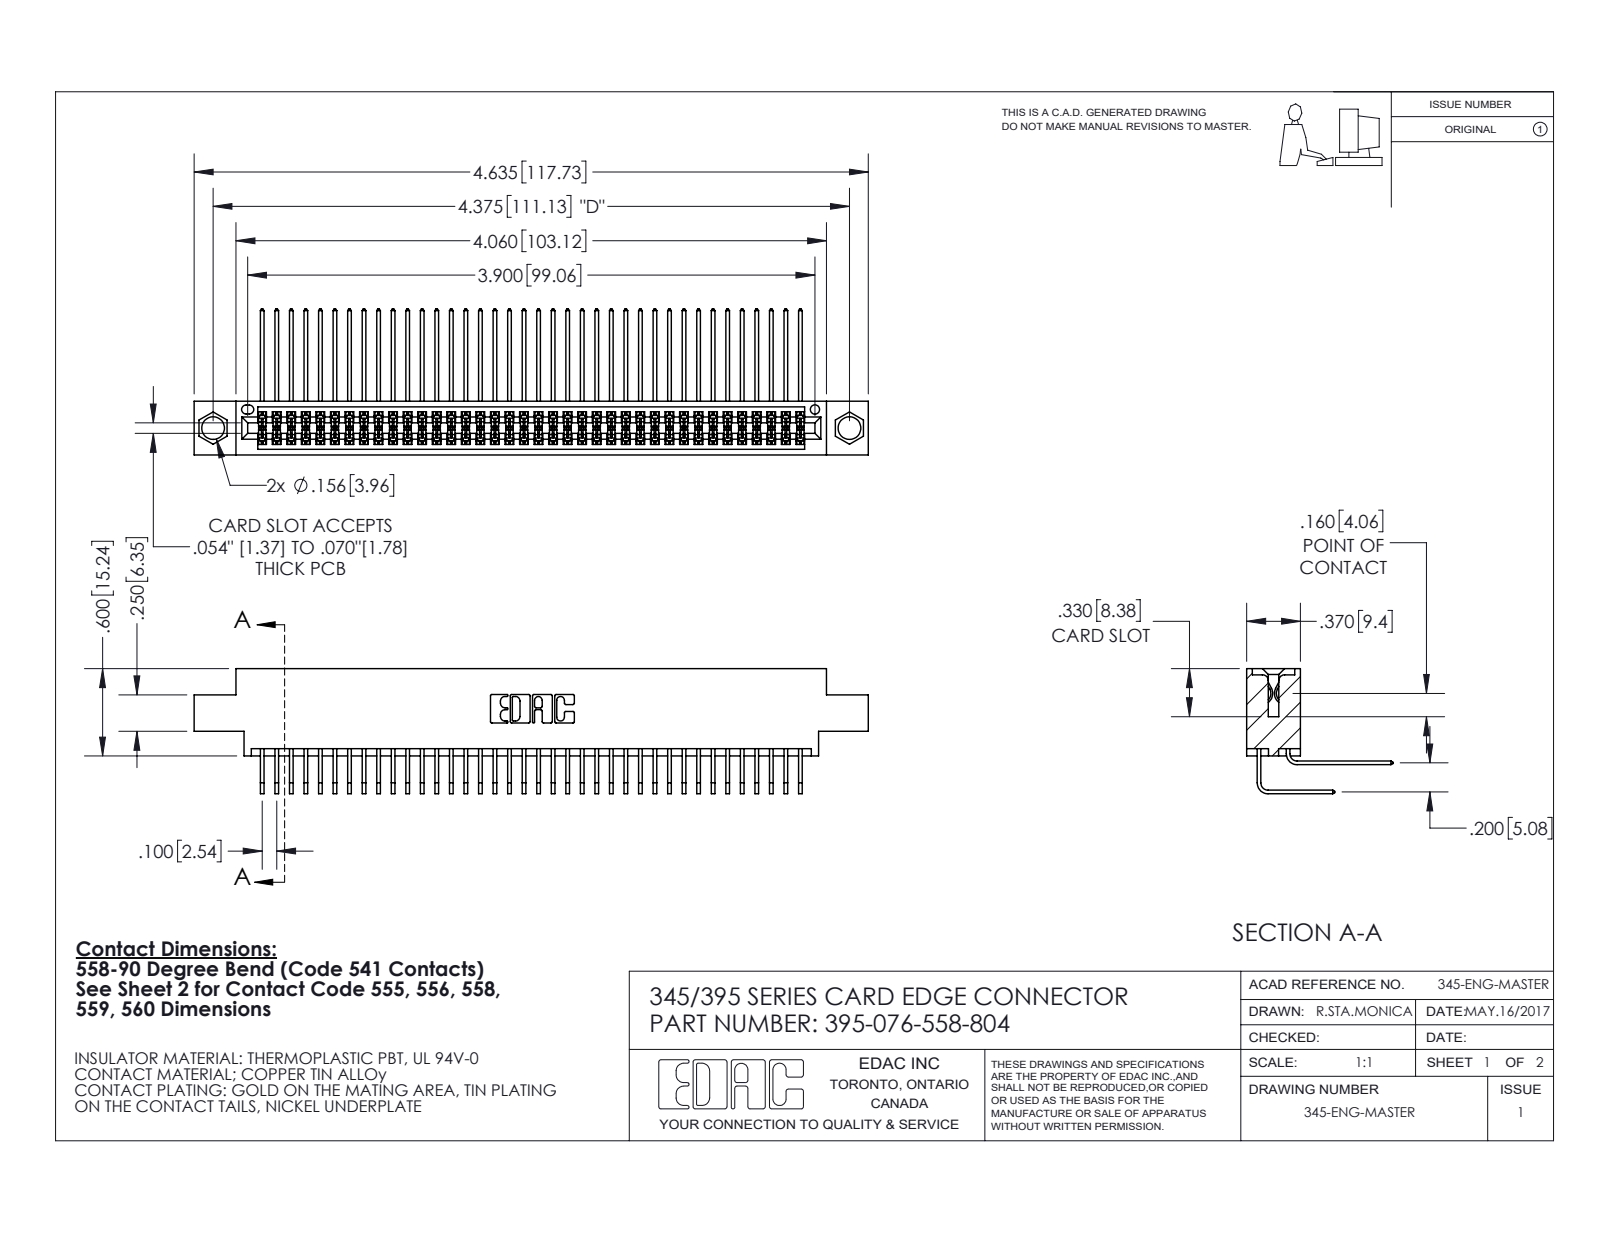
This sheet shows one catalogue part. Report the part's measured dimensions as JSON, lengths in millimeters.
{"part_name": "345-292-001_558 559 Tail - 1; 345-292-001_558 Tail - 2; 395-076-558-804; 345 Part_0.170 Offset - 0.156 Dia-TI", "step_written_by": "SolidWorks 2020 (CONFIG_CONTROL_DESIGN)", "units": "millimeters", "bodies": {"solids": 77, "faces": 4096, "planar": 2758, "cylindrical": 1338, "other": 0}, "overall_size": [117.7, 25.5, 21.8], "volume_mm3": 11600, "surface_area_mm2": 19150, "round_holes": [[4, 2], [1.6, 1]], "partial_cylinders_radius": [[0.2, 114], [0.3, 22], [0.2, 6], [0.8, 6], [0.7, 3], [0.4, 2], [0.5, 2], [0.6, 2]], "face_to_face_distances": [1.8, 7.6, 5.1, 9.4, 2.5, 6.9, 0.6, 5.7, 4.4, 0.6], "hole_center_spacings": [6.9, 105.1, 111.1]}
